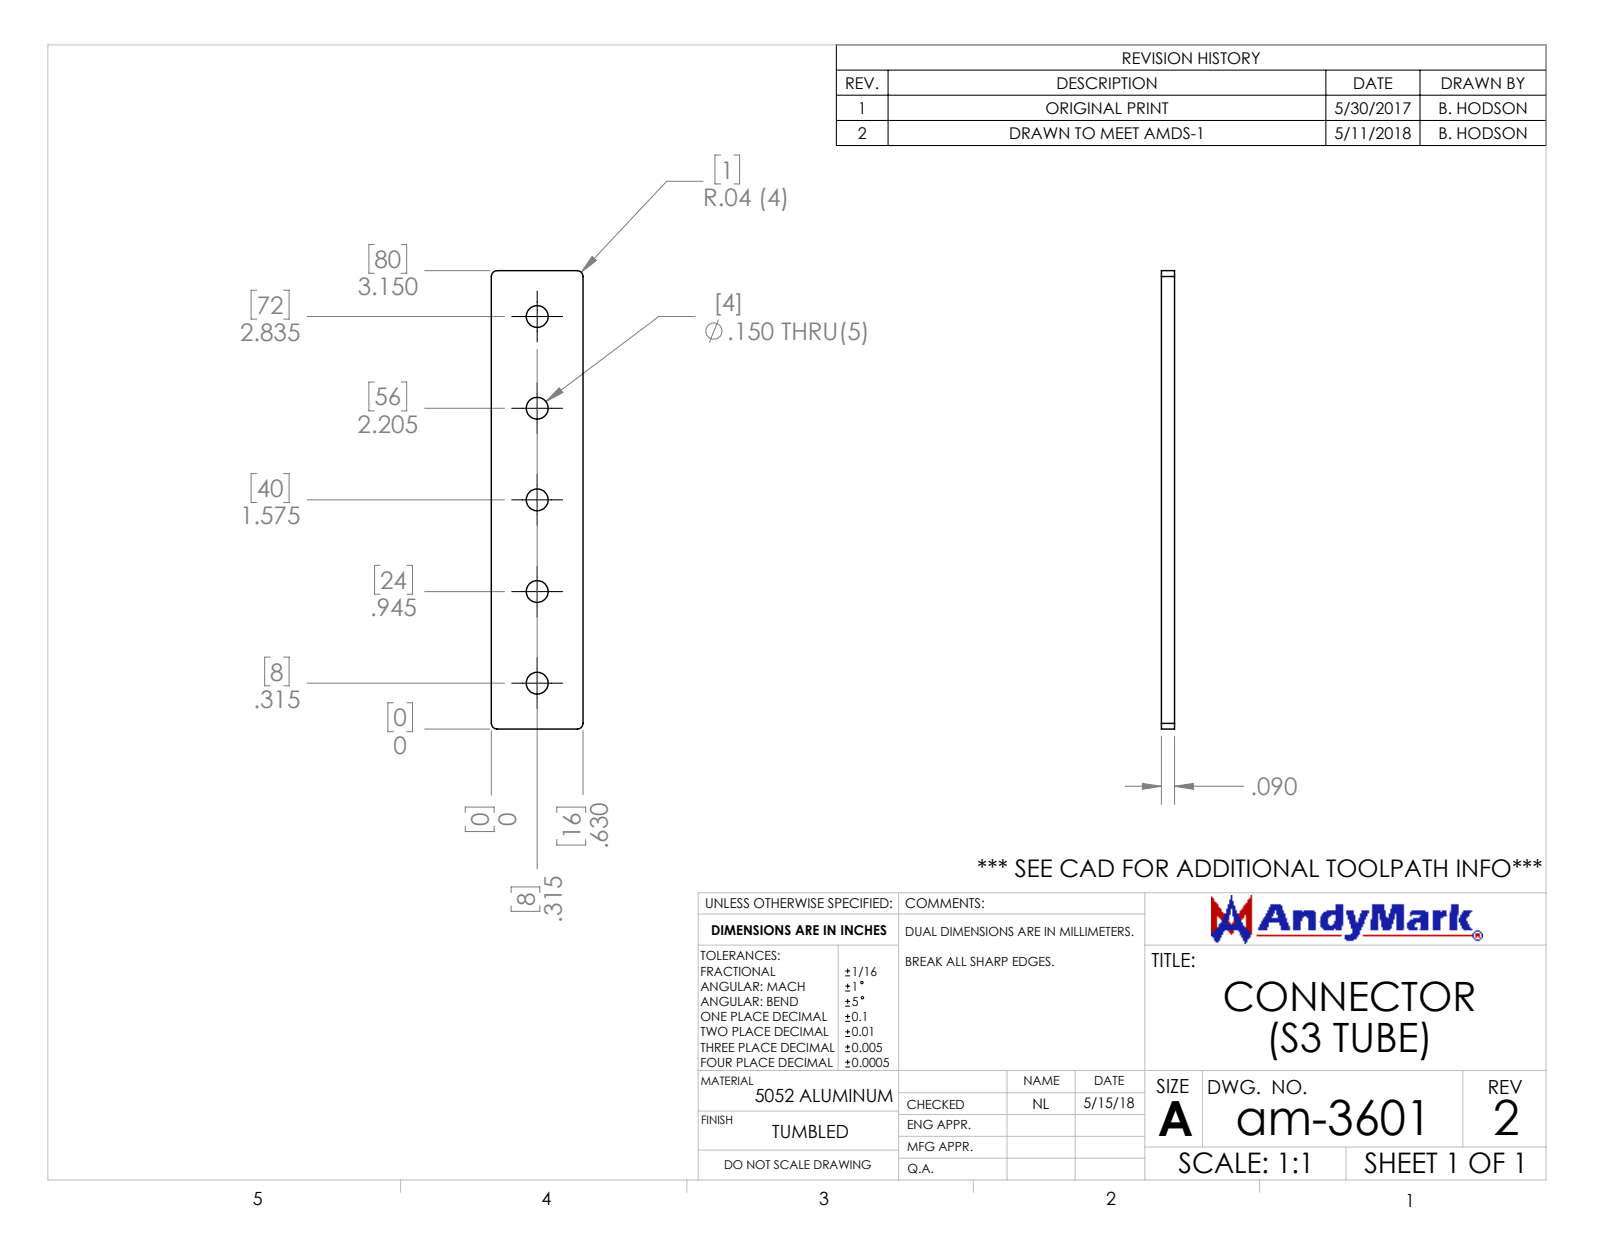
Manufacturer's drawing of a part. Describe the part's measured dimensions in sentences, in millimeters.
The part is named "am-3601 Connector (S3 Tube) REV2". Its 3-D file was written by "SolidWorks 2017 (AUTOMOTIVE_DESIGN)". It is 1 solid with 20 faces: 6 planar, 14 cylindrical and 0 other. Overall it measures 80 by 16 by 2.29 millimeters. Its volume is 2 794 cubic millimeters and its surface area 3 016 square millimeters. Round holes: 5 of diameter 3.81. Partial cylindrical surfaces (rounded edges, fillets, slot ends): 4 of radius 1. The main face-to-face distances are 2.29, 16, 80. The hole center spacings are 16, 32, 48, 64.
